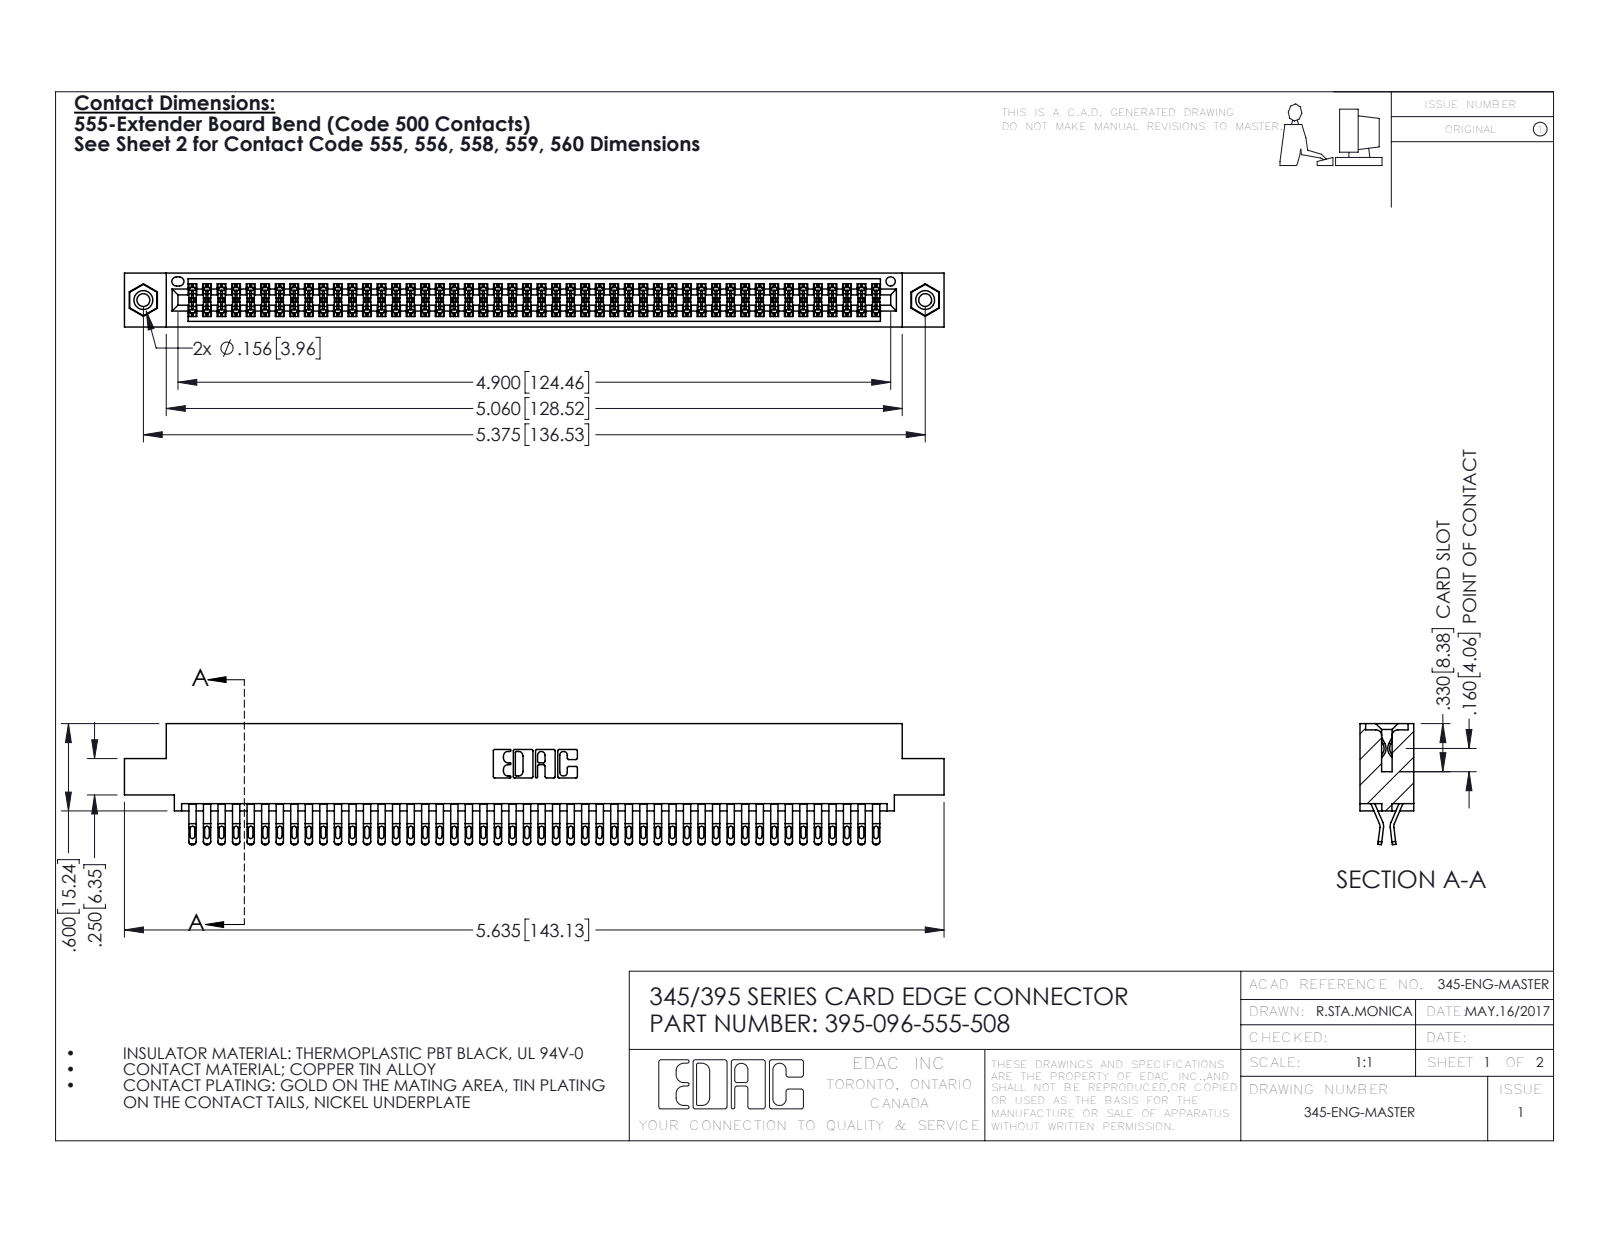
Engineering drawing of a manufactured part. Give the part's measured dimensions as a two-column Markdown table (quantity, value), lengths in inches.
| quantity | value |
| --- | --- |
| part name | 345-250-001_345-250-003-102; 395-096-555-508; 345 Part_0.110 Offset - 0.156 Dia-TI; 345-292-001_555 Tail |
| STEP written by | SolidWorks 2016 (CONFIG_CONTROL_DESIGN) |
| units | inches |
| bodies | 99 solids, 5566 faces (3092 planar, 2458 cylindrical, 16 other) |
| overall size | 5.635 × 0.832 × 0.37 |
| volume | 0.864 in³ |
| surface area | 34.28 in² |
| round holes (diameter × count) | 0.089 × 2, 0.125 × 2, 0.156 × 2, 0.064 × 1 |
| round bosses / shafts (diameter × count) | 0.155 × 2 |
| partial cylindrical surfaces (radius × count) | 0.016 × 240, 0.02 × 192, 0.006 × 144, 0.01 × 22, 0.007 × 6, 0.031 × 6, 0.026 × 3, 0.01 × 2 |
| main face-to-face distances | 0.072, 0.298, 0.025, 0.37, 0.2, 0.098, 0.272, 0.225, 0.175, 0.149 |
| hole center spacings | 0.27, 5.139, 5.375 |
